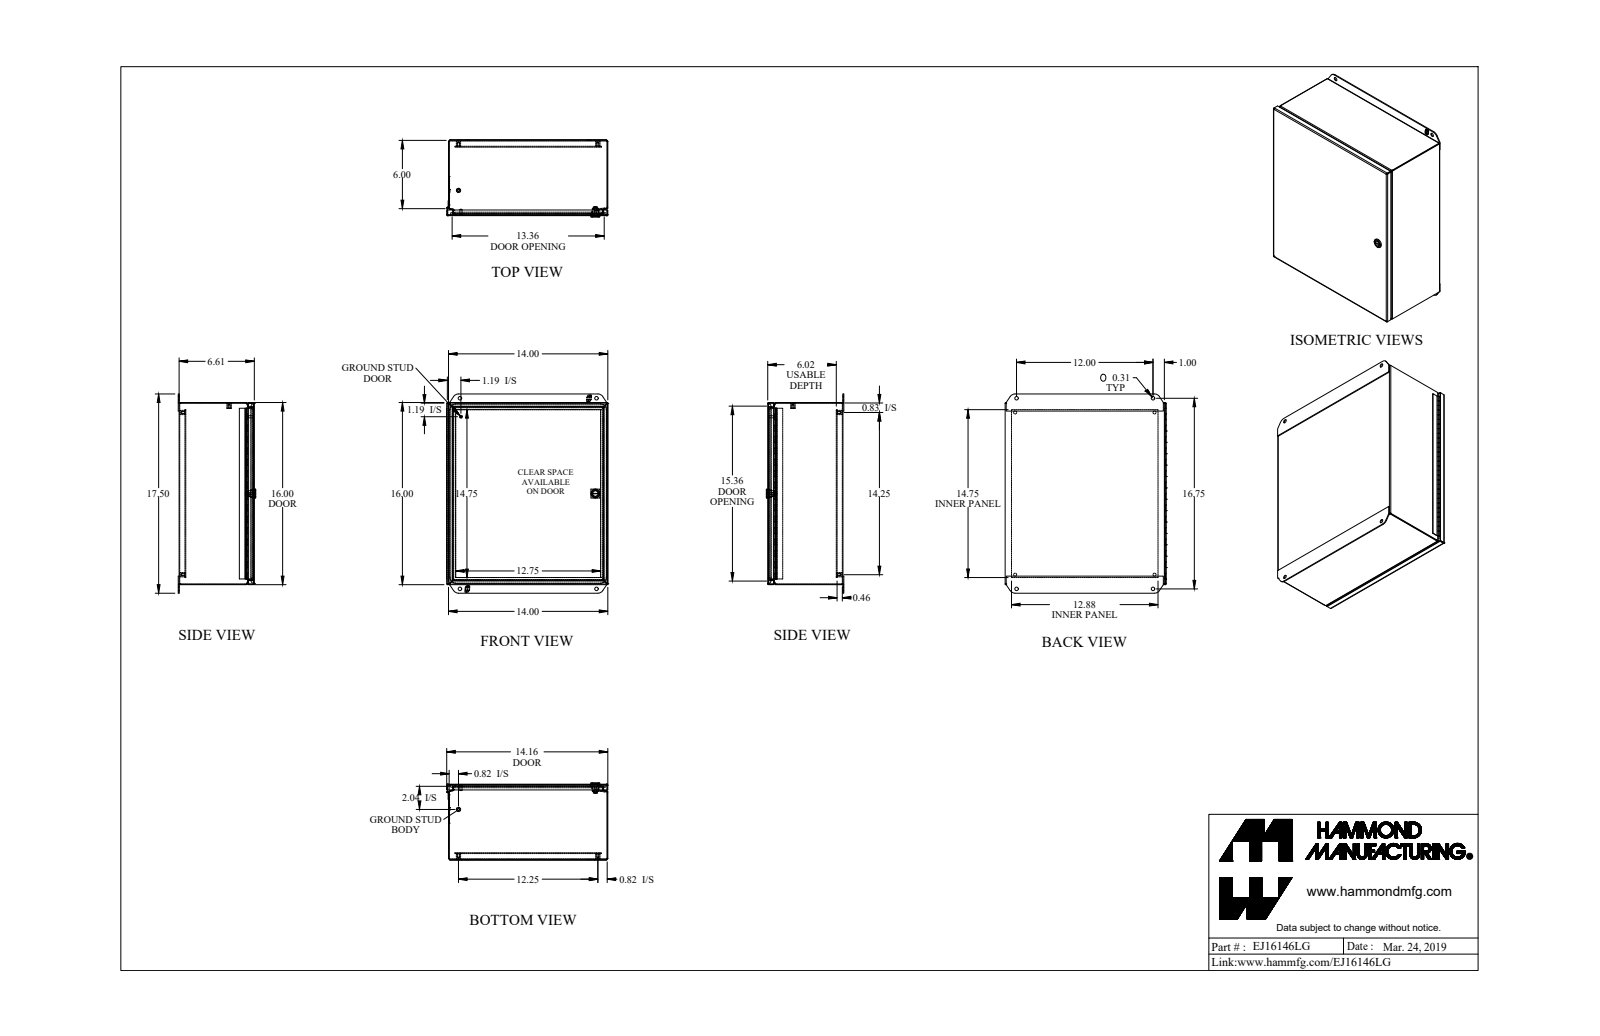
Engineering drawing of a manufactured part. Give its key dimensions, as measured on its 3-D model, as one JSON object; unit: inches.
{"part_name": "EJ16146LG_Default", "step_written_by": "SolidWorks 2019 (CONFIG_CONTROL_DESIGN)", "units": "inches", "bodies": {"solids": 16, "faces": 771, "planar": 425, "cylindrical": 254, "other": 92}, "overall_size": [17.5, 14.165, 6.805], "volume_in3": 72.85, "surface_area_in2": 2402, "round_holes": [[0.156, 5], [0.265, 4], [0.313, 4], [0.05, 1], [0.516, 1]], "round_bosses_or_shafts": [[0.375, 5], [0.788, 1], [0.535, 1], [0.496, 1], [0.435, 1], [0.25, 1], [0.188, 1], [0.1, 1]], "partial_cylinders_radius": [[0.029, 16], [0.086, 16], [0.281, 10], [0.25, 4], [0.499, 4], [0.5, 4], [0.06, 2], [0.539, 2]], "face_to_face_distances": [0.057, 6.554, 0.072, 0.589, 6.611, 6.497, 0.46, 0.517, 6.094, 6.037], "hole_center_spacings": [1.256, 15.5, 19.679, 14.25, 12.189, 7.128, 8.375, 12]}
